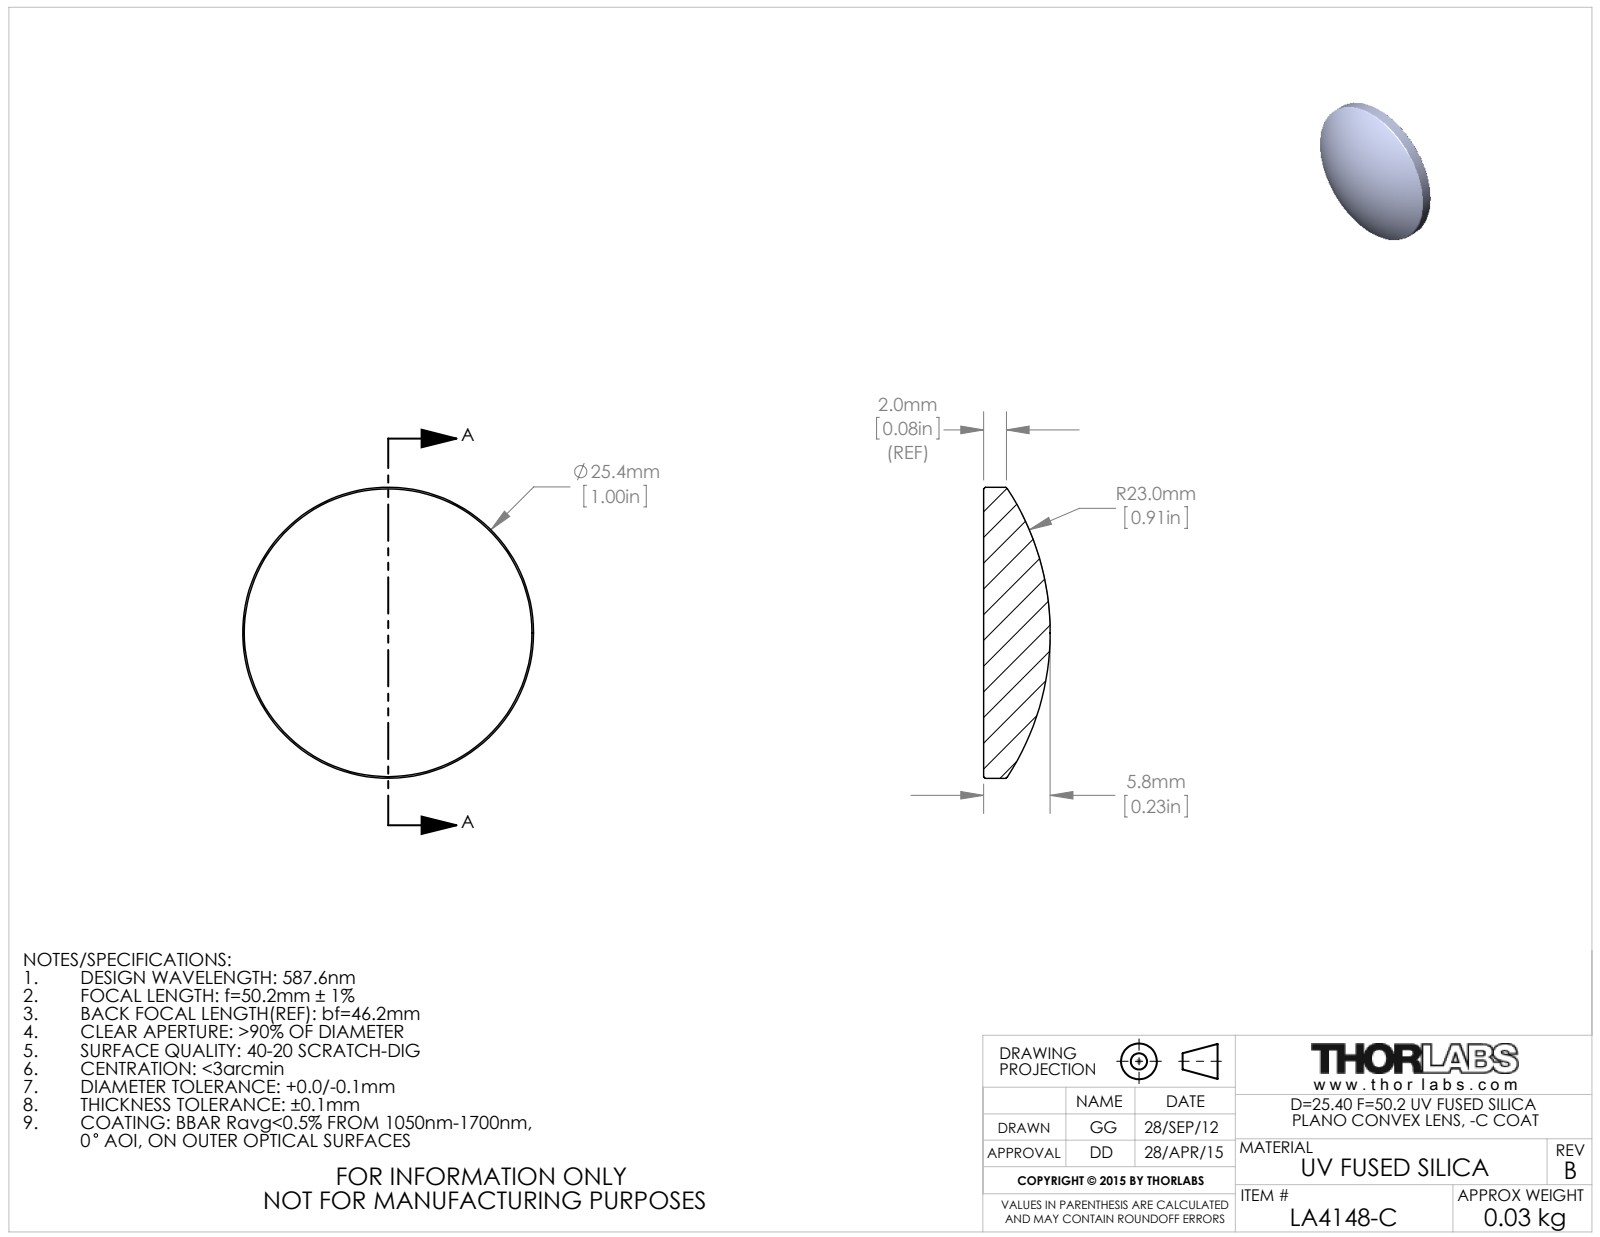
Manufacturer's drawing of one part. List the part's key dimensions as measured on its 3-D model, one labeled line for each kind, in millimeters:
Part name (STEP PRODUCT): 24974-E0W
STEP written by: SolidWorks 2014 (CONFIG_CONTROL_DESIGN)
Units: millimetres
Bodies: 1 solid, 9 faces (1 planar, 2 cylindrical, 6 other)
Overall size (bounding box): 25.4 × 25.4 × 5.82
Volume: 2 010 mm³ · Surface area: 1 211 mm²
Round bosses / shafts (diameter × count): ⌀25.4 ×1
